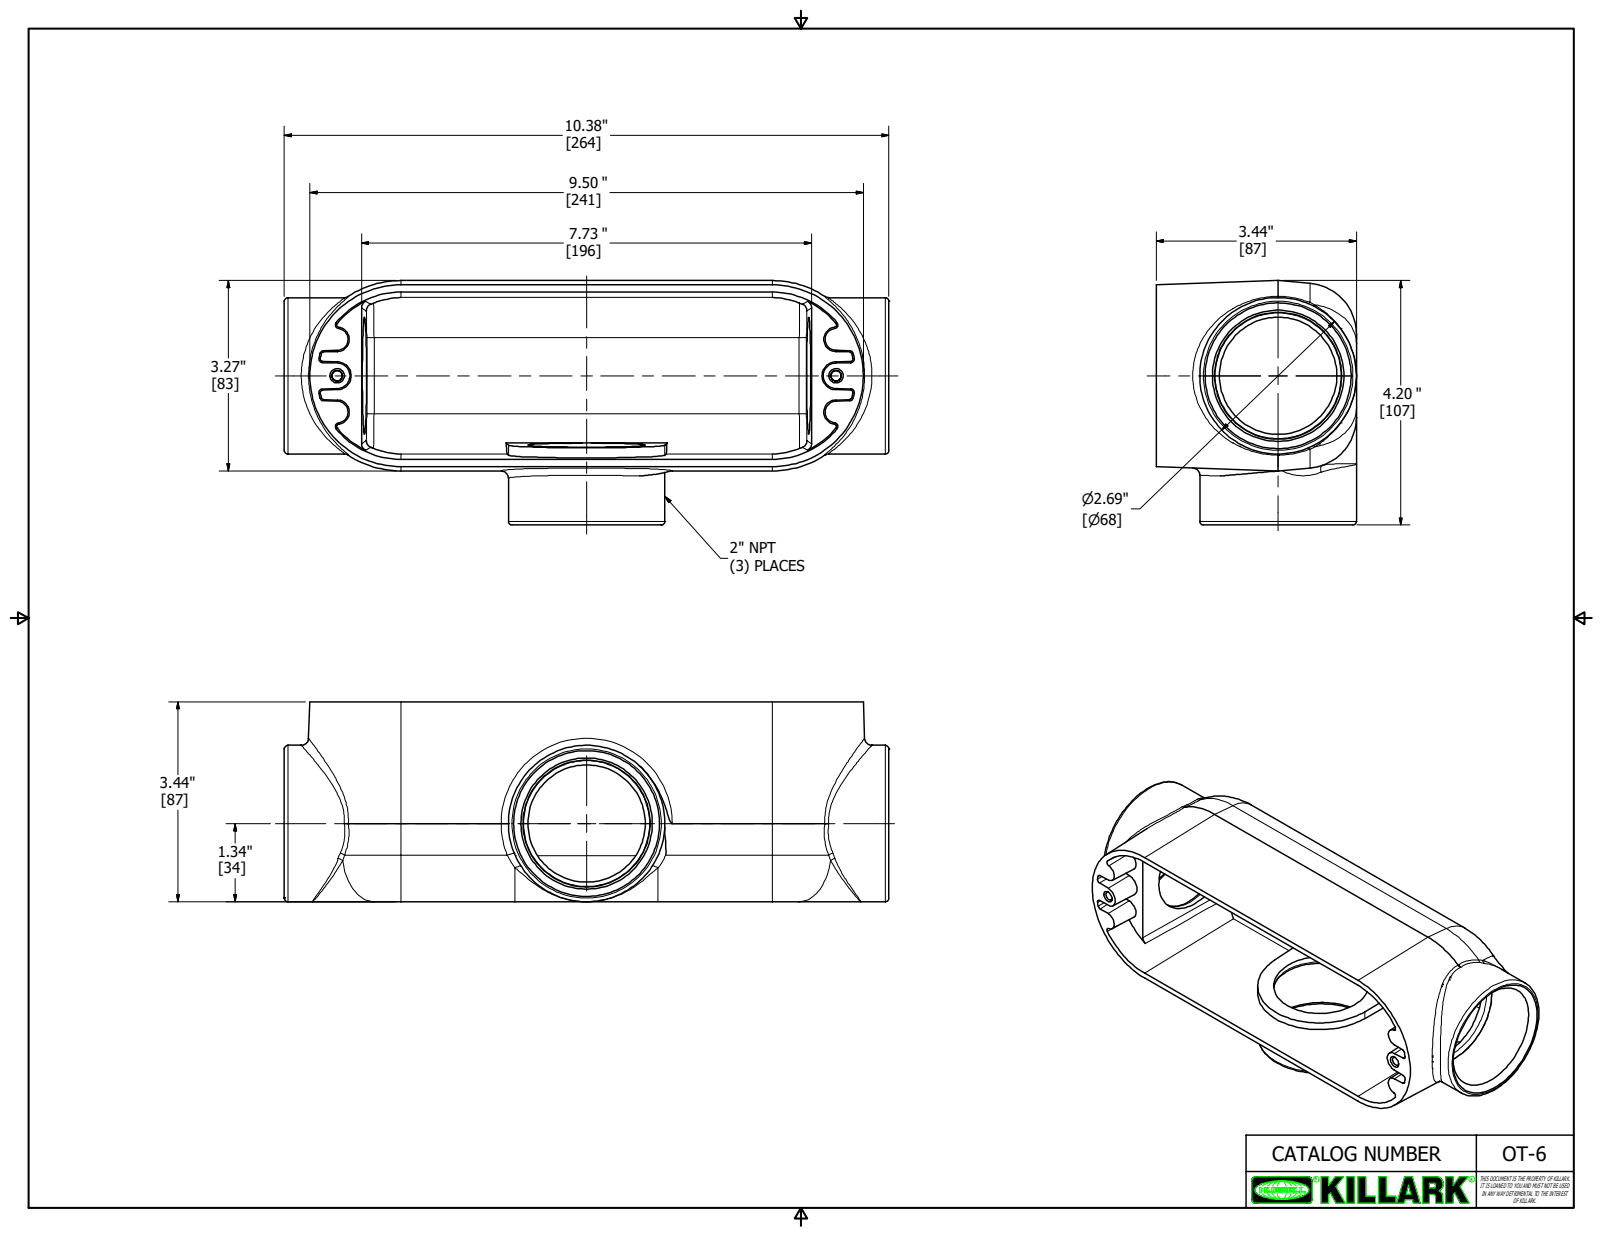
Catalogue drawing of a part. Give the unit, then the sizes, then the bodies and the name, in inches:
Units: inches
Overall size (bounding box): 10.375 × 4.203 × 3.438
Round holes (diameter × count): ⌀2.014 ×2
Round bosses / shafts (diameter × count): ⌀2.687 ×2
Partial cylindrical surfaces — rounded edges, fillets, slot ends (radius × count): R0.031 ×2, R0.125 ×2, R0.687 ×2, R0.875 ×2
Main face-to-face distances: 2.997, 2.997, 0.125, 3.437, 3.313, 0.172, 2.826, 2.813, 2.688, 0.625
Volume: 22.51 in³ · Surface area: 216.5 in²
Bodies: 1 solid, 151 faces (43 planar, 16 cylindrical, 92 other)
Part name (STEP PRODUCT): 17222-1
STEP written by: Autodesk Inventor 2018 (AUTOMOTIVE_DESIGN)
